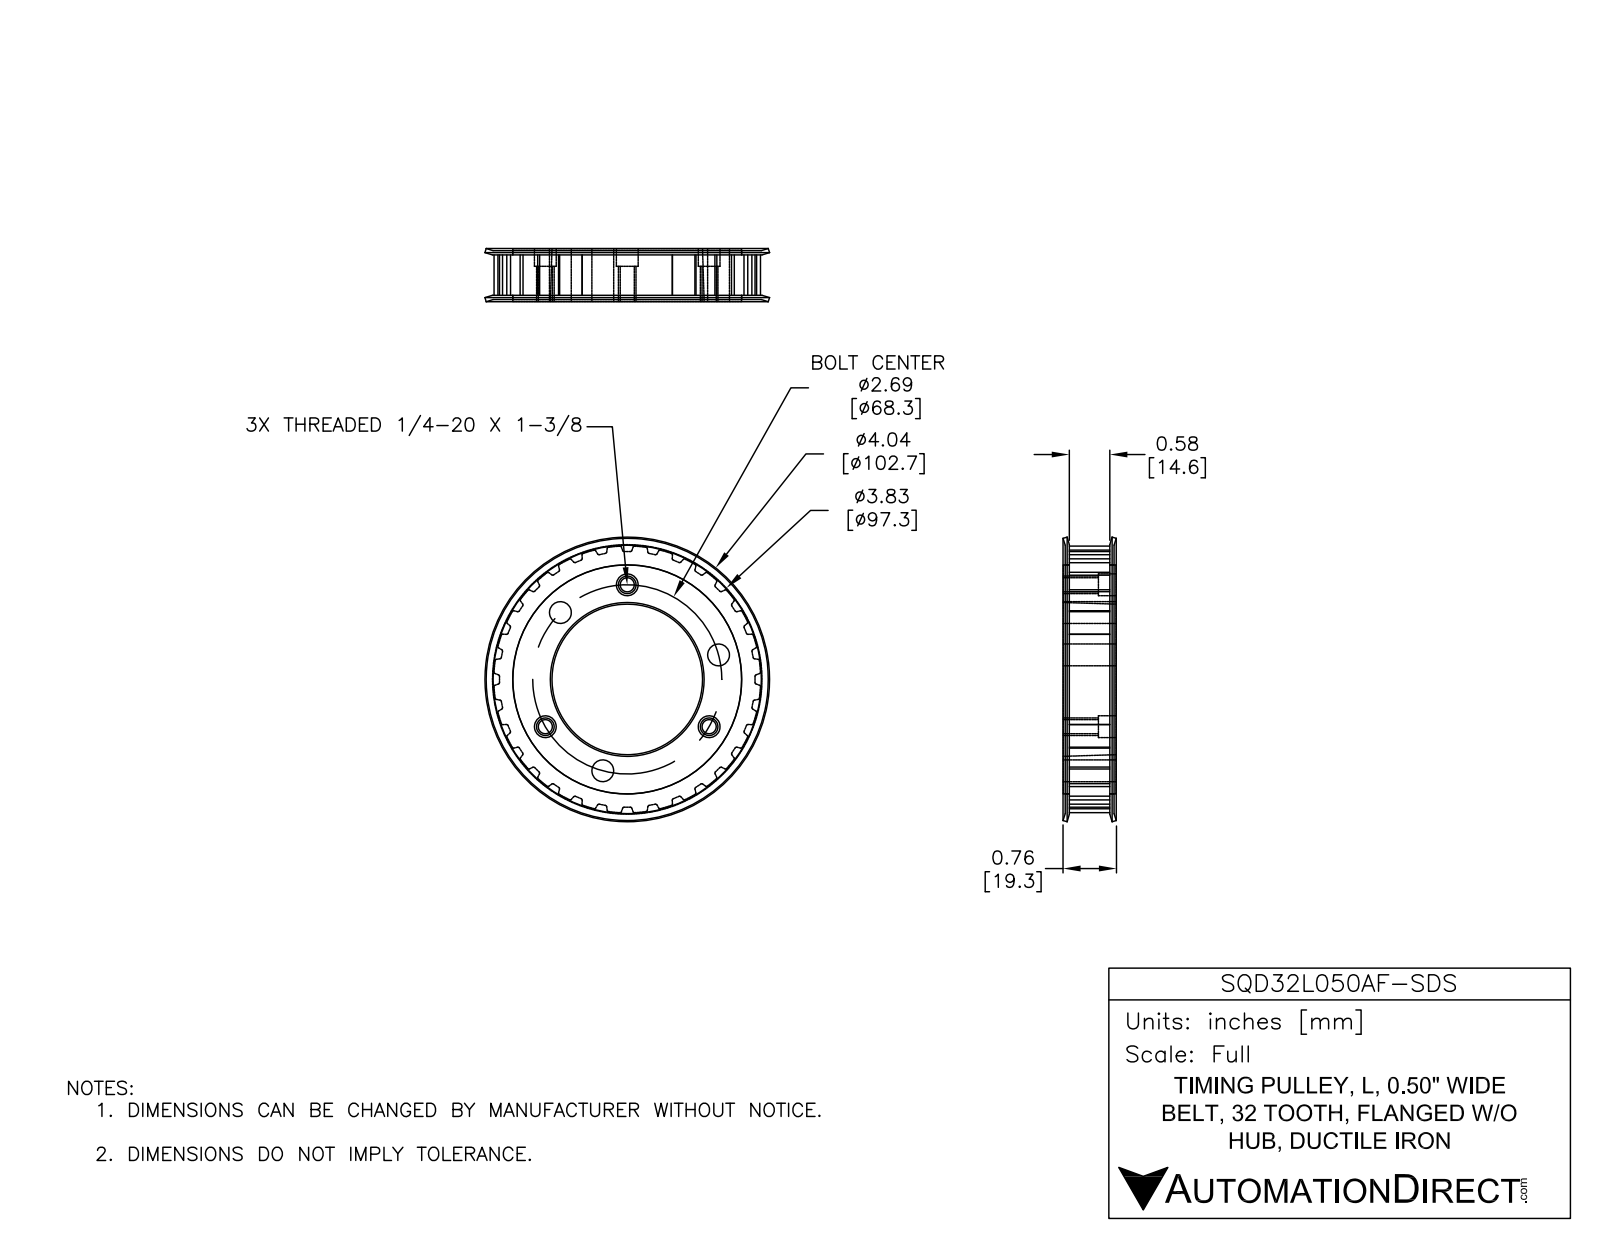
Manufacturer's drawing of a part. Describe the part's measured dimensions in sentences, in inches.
The part is named "SQD32L050AF-SDS". Its 3-D file was written by "SolidWorks 2018 (AUTOMOTIVE_DESIGN)". It is 1 solid with 333 faces: 107 planar, 212 cylindrical and 14 other. Overall it measures 4.044 by 4.044 by 0.755 inches. Its volume is 5.238 cubic inches and its surface area 43.45 square inches. Round holes: 6 of diameter 0.31, 3 of diameter 0.2, 1 of diameter 3.254. Round bosses or shafts: 1 of diameter 3.25. Partial cylindrical surfaces (rounded edges, fillets, slot ends): 64 of radius 0.015, 64 of radius 0.02, 1 of radius 1.896. The main face-to-face distances are 0.75, 0.028, 0.723, 0.695, 0.722, 0.027, 0.06, 0.635, 0.663, 0.087. The hole center spacings are 1.344, 1.029, 1.343, 1.636, 2.328, 2.328, 2.665, 1.028.
